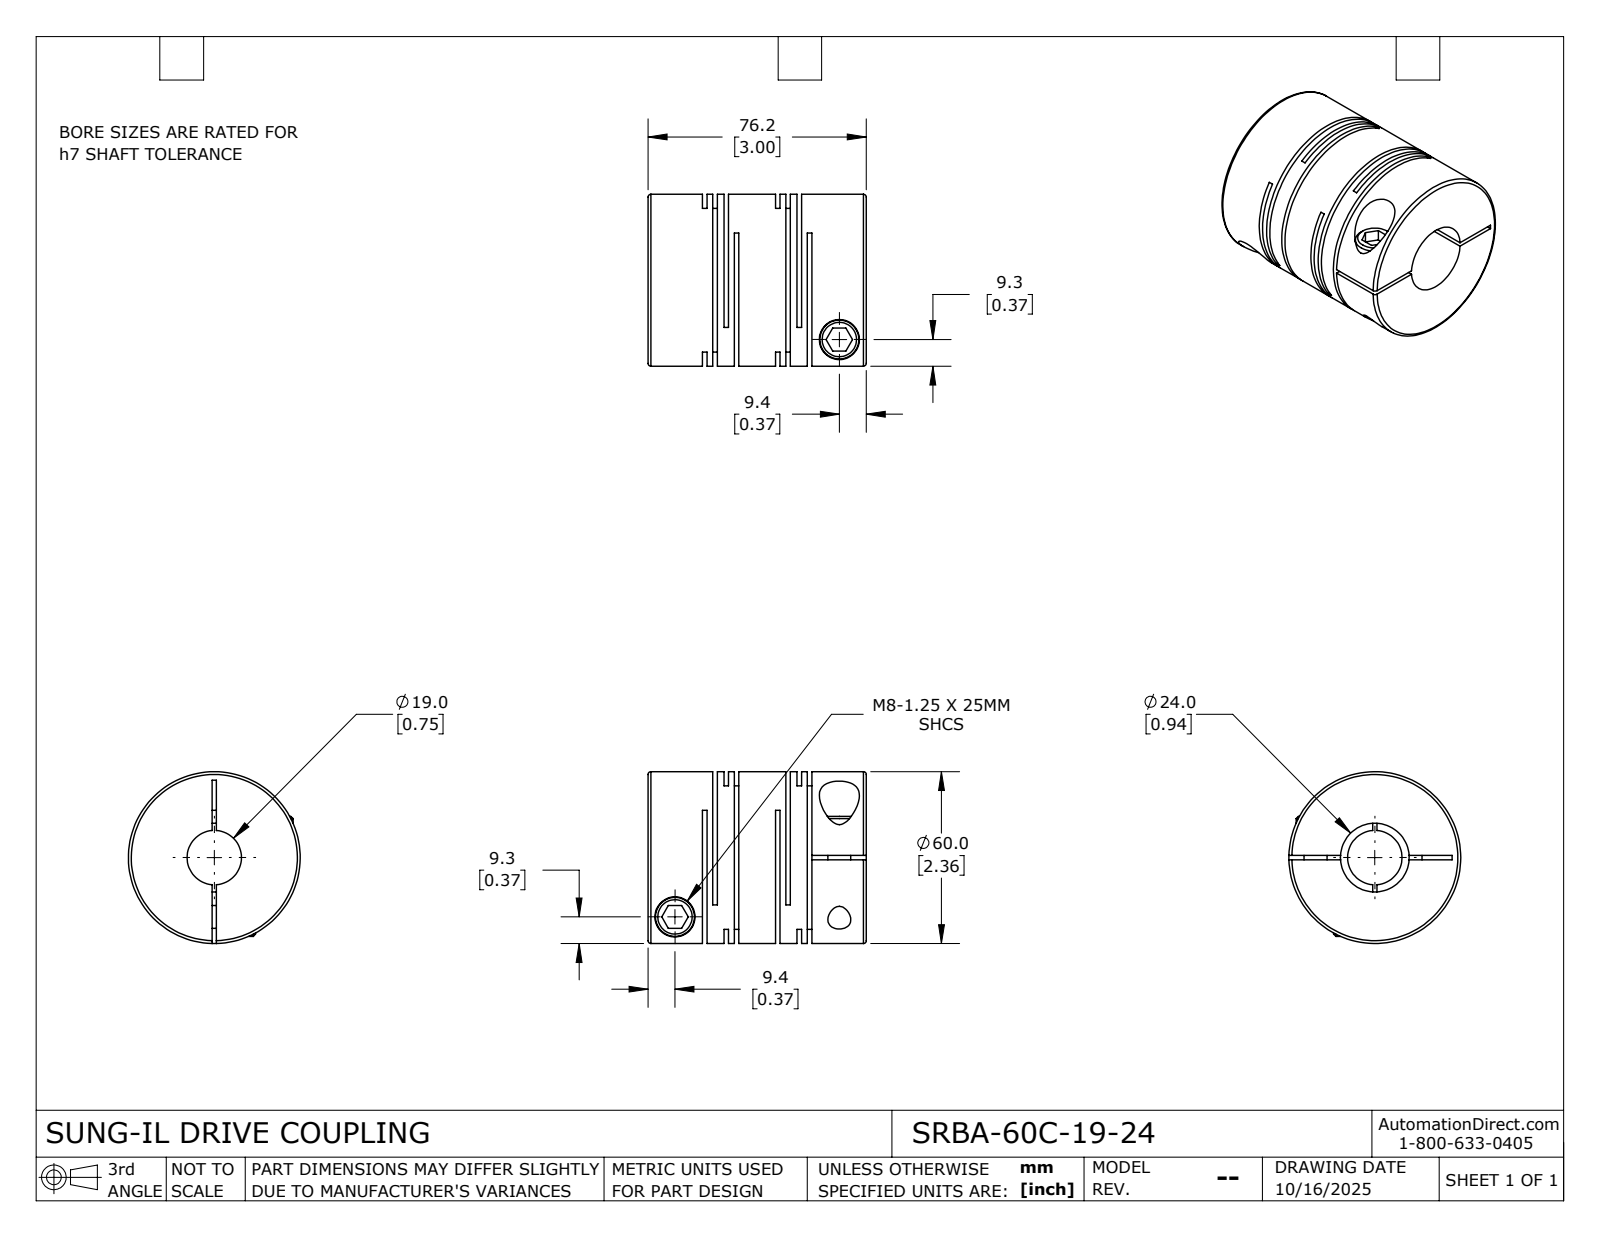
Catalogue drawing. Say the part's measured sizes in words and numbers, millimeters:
The part is named "SRBA-60C-19-24". Its 3-D file was written by "SolidWorks 2024 (CONFIG_CONTROL_DESIGN)". It is 1 solid with 115 faces: 60 planar, 42 cylindrical and 13 other. Overall it measures 76.2 by 60 by 60 millimeters. Its volume is 154 808 cubic millimeters and its surface area 57 364 square millimeters. Round holes: 2 of diameter 8, 2 of diameter 14, 1 of diameter 19, 1 of diameter 24. Round bosses or shafts: 2 of diameter 13.6, 1 of diameter 60. The main face-to-face distances are 1.6, 3.6, 7.5, 25.5, 33, 27.1, 2, 5.9, 23.9, 3.9.
